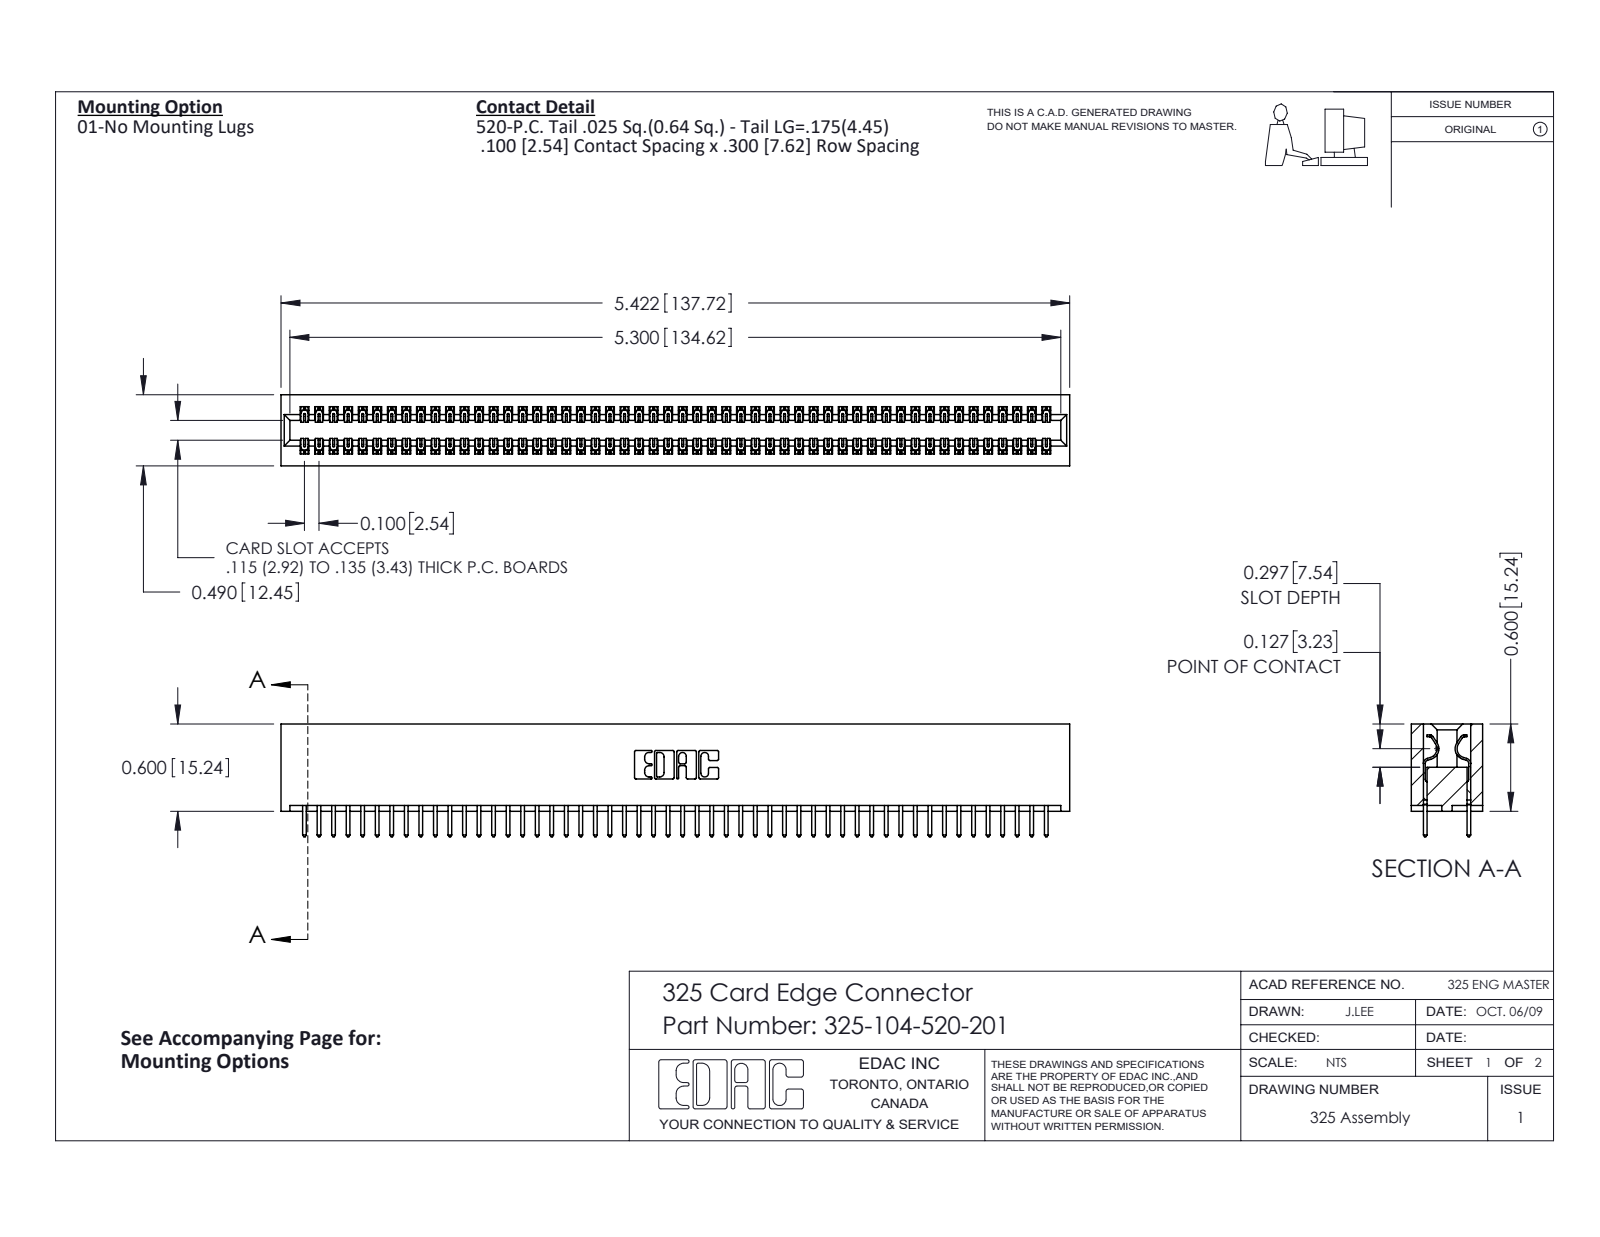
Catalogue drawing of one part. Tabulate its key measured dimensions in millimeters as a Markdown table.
| quantity | value |
| --- | --- |
| part name | 325-292-001_325-293-120; 325 Part_Lugless; 325-104-520-201 |
| STEP written by | SolidWorks 2016 (CONFIG_CONTROL_DESIGN) |
| units | millimeters |
| bodies | 105 solids, 5514 faces (3810 planar, 1704 cylindrical, 0 other) |
| overall size | 137.7 × 19.7 × 12.4 |
| volume | 18 450 mm³ |
| surface area | 23 030 mm² |
| partial cylindrical surfaces (radius × count) | 0.2 × 156, 0.3 × 104, 0.3 × 22, 0.2 × 6, 0.8 × 6, 0.7 × 3, 0.4 × 2, 0.6 × 2 |
| main face-to-face distances | 2.1, 10.3, 7.6, 12.4, 2.7, 9.7, 0.6, 8.3, 7, 14.2 |
